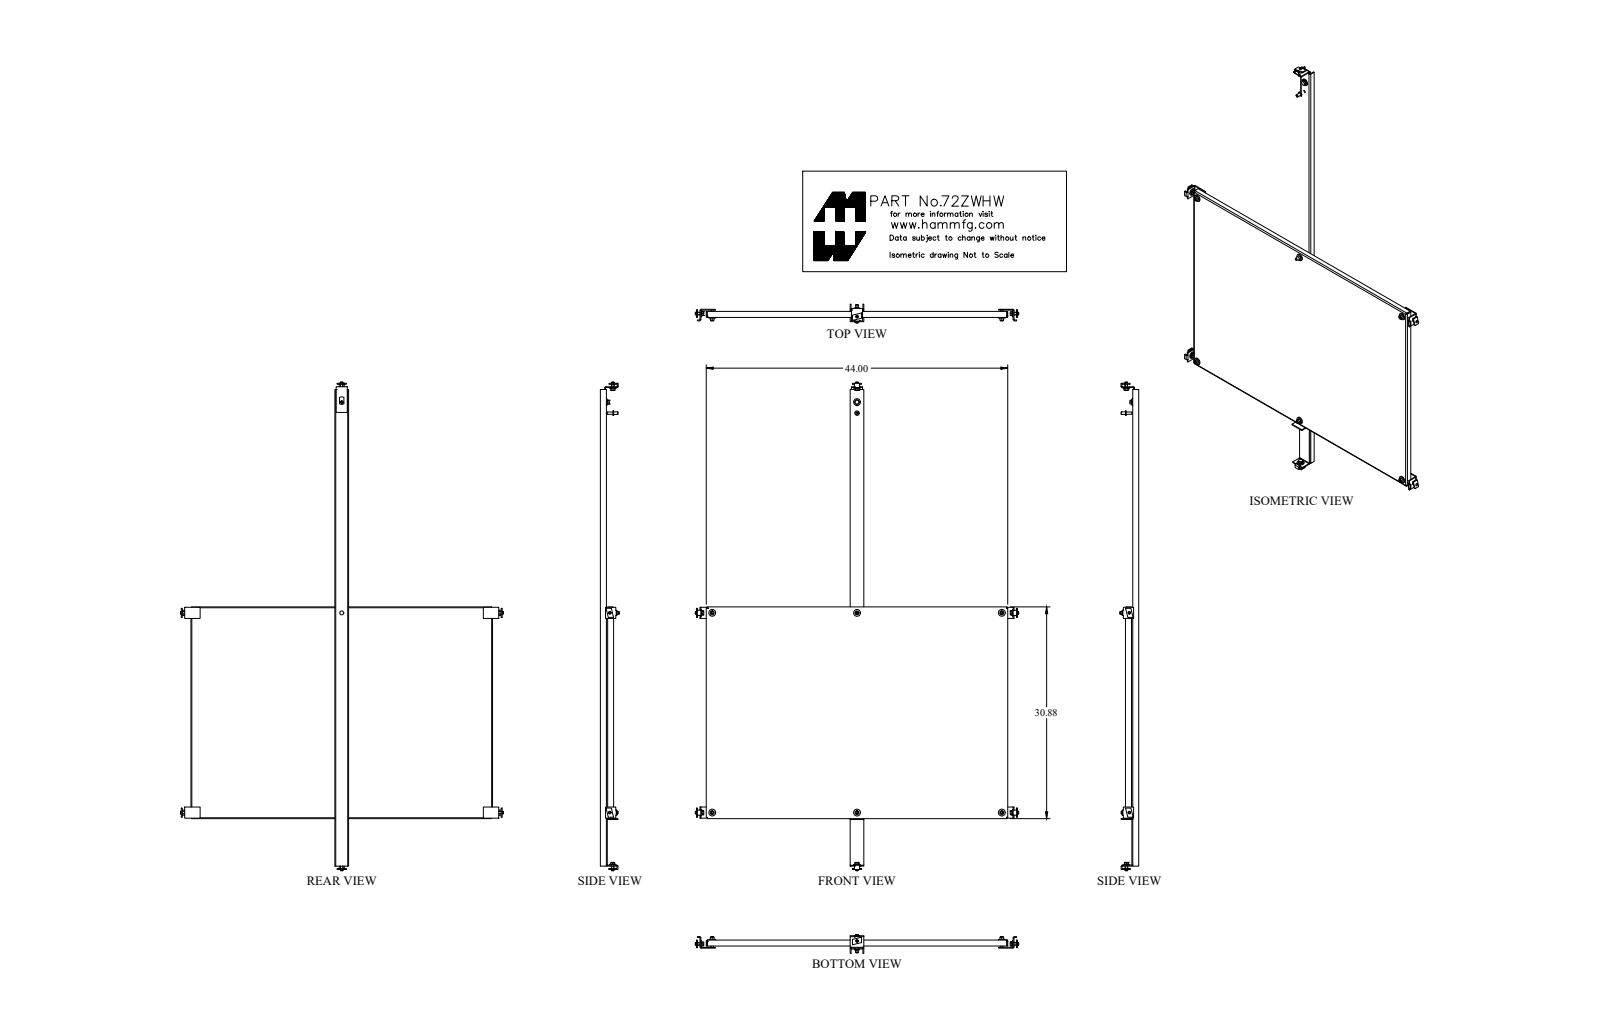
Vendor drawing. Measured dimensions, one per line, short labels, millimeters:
name: 72ZWHW_Default
written by: SolidWorks 2018 (CONFIG_CONTROL_DESIGN)
unit: mm
bodies: 1 solid, 60 faces (34 planar, 20 cylindrical, 6 other)
size: 1117.6 × 784.2 × 22.2
volume: 2 992 000 mm³; area: 1 898 000 mm²
holes: 6× ⌀14.3
rounds: 4× R1.5, 4× R4.7
face distances: 3.2, 781.1, 1114.4, 777.9, 784.2, 1117.6, 1111.3, 22.2, 19.1, 3.2
hole spacings: 536.6, 913.9, 739.8, 1073.2, 1303.4
